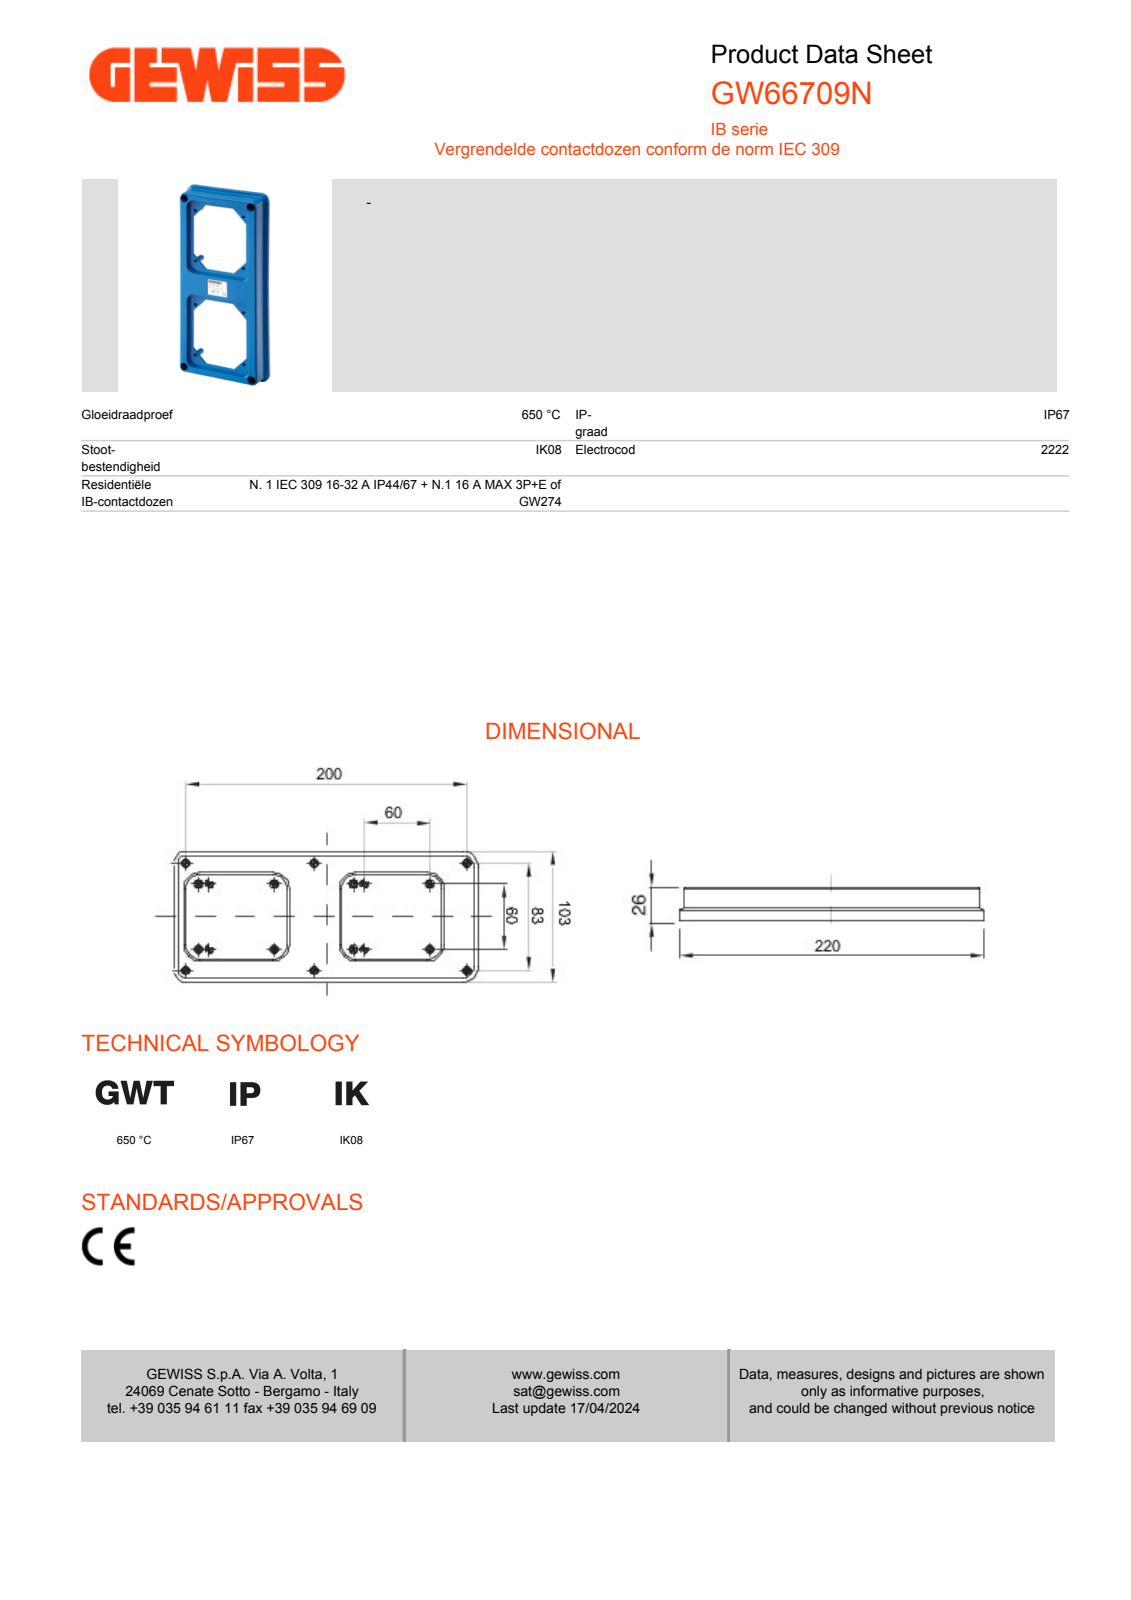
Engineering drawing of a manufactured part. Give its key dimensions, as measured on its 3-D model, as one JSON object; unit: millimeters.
{"part_name": "GW66709N", "step_written_by": "CREO PARAMETRIC BY PTC INC, 2020354 (CONFIG_CONTROL_DESIGN)", "units": "millimeters", "bodies": {"solids": 1, "faces": 182, "planar": 88, "cylindrical": 34, "other": 60}, "overall_size": [220, 103, 26], "volume_mm3": 97626, "surface_area_mm2": 66345, "partial_cylinders_radius": [[1.5, 10], [0.3, 6], [2, 4], [6.4, 4], [10, 4], [34, 2], [36.5, 2]], "face_to_face_distances": [2.4, 6, 5.5, 0.5, 26, 18.1, 7.9, 3.6, 20.5, 23.6]}
